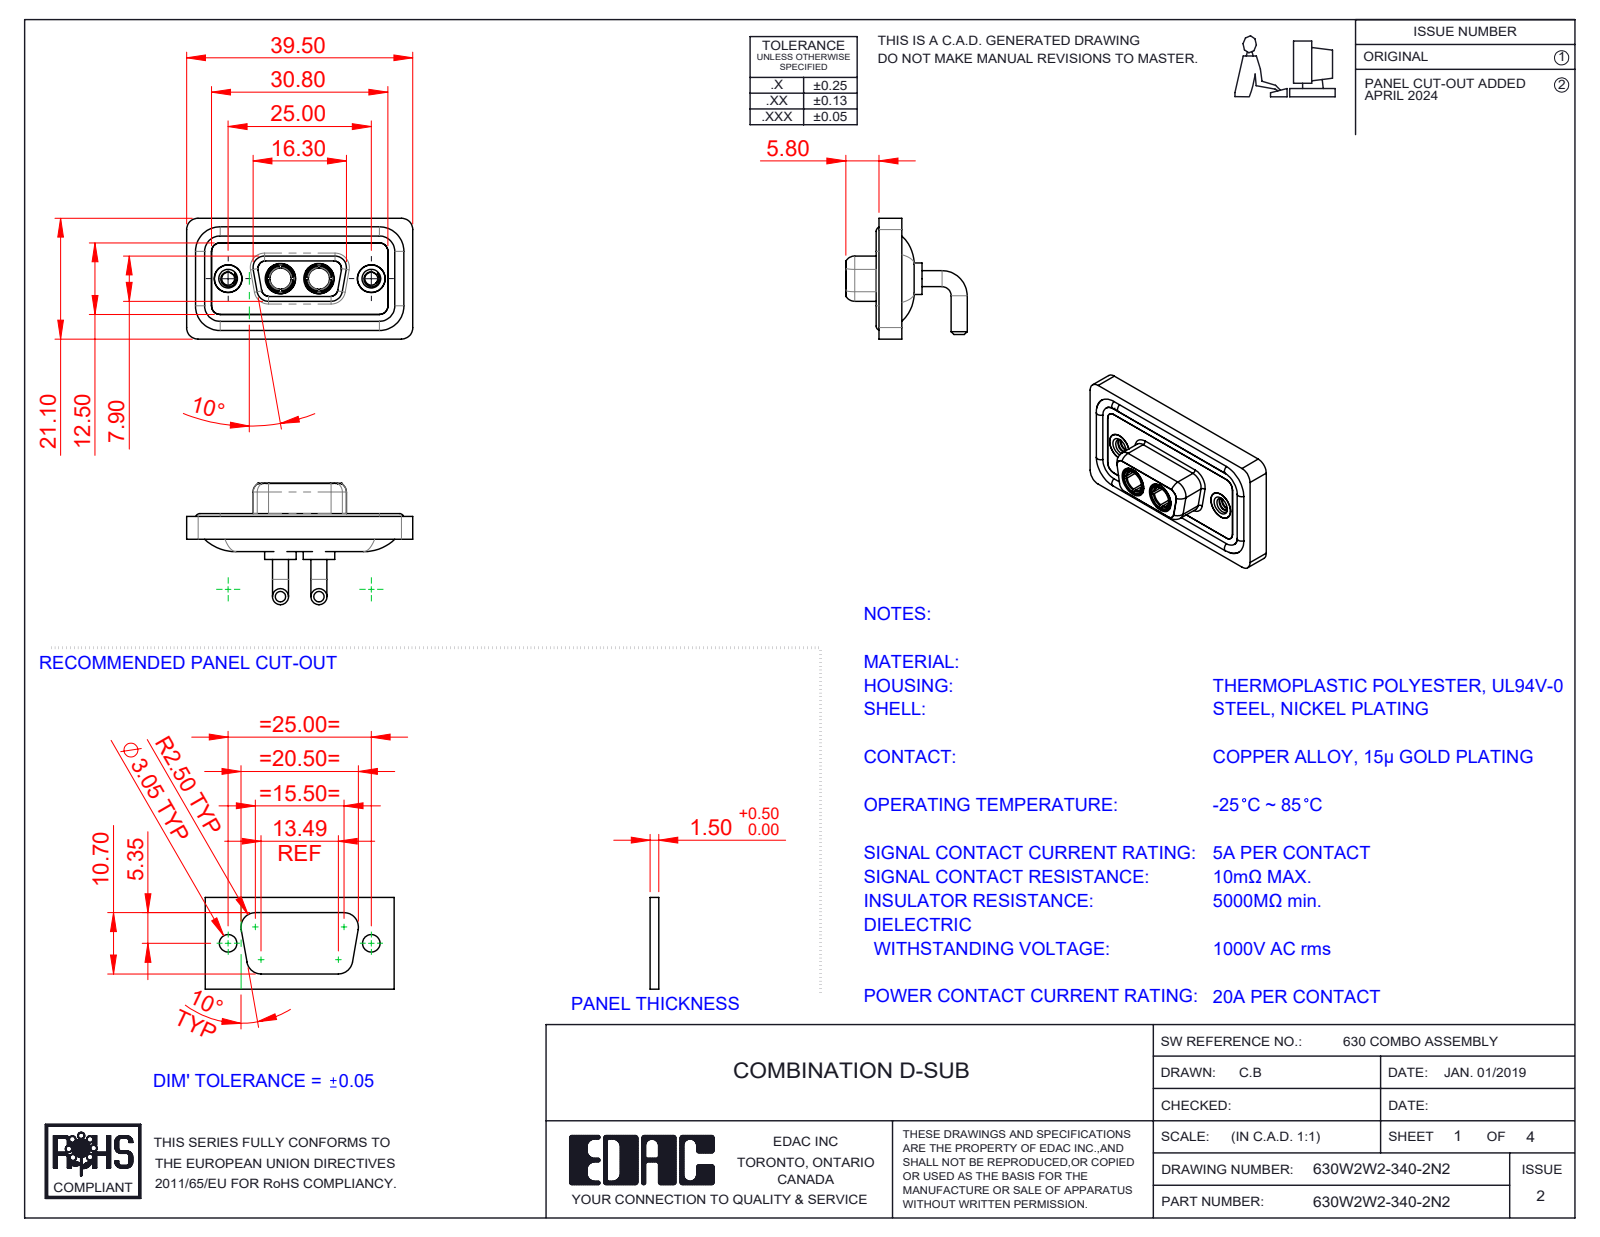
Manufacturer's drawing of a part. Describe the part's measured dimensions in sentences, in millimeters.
The part is named "630Combo Shell Rear_09 Contacts; 630Combo Housing_2W2; 630Combo Shell Front_09 Contacts; 630Combo Waterproof Housing_09 Contacts (+3 more)". Its 3-D file was written by "SolidWorks 2023 (CONFIG_CONTROL_DESIGN)". It is 11 solids with 542 faces: 163 planar, 238 cylindrical and 141 other. Overall it measures 39.5 by 21.2 by 21.1 millimeters. Its volume is 4 816 cubic millimeters and its surface area 7 786 square millimeters. Round holes: 4 of diameter 4.85, 2 of diameter 2.26, 2 of diameter 3.7, 2 of diameter 4, 2 of diameter 4.05, 2 of diameter 5, 2 of diameter 5.3. Round bosses or shafts: 4 of diameter 2.8, 4 of diameter 1.6, 2 of diameter 5.5, 2 of diameter 5.2, 2 of diameter 4.96, 2 of diameter 4.95, 2 of diameter 4.8, 2 of diameter 4.75. Partial cylindrical surfaces (rounded edges, fillets, slot ends): 18 of radius 1.5, 18 of radius 2, 8 of radius 1.35, 8 of radius 1.6, 4 of radius 0.25, 4 of radius 0.5, 4 of radius 0.6, 4 of radius 0.65. The main face-to-face distances are 0.4, 1.8, 1.1, 2.9, 2.5, 1.6, 3.1, 1.5, 2.1, 0.5. The hole center spacings are 9.14, 15.86, 6.72, 25.
